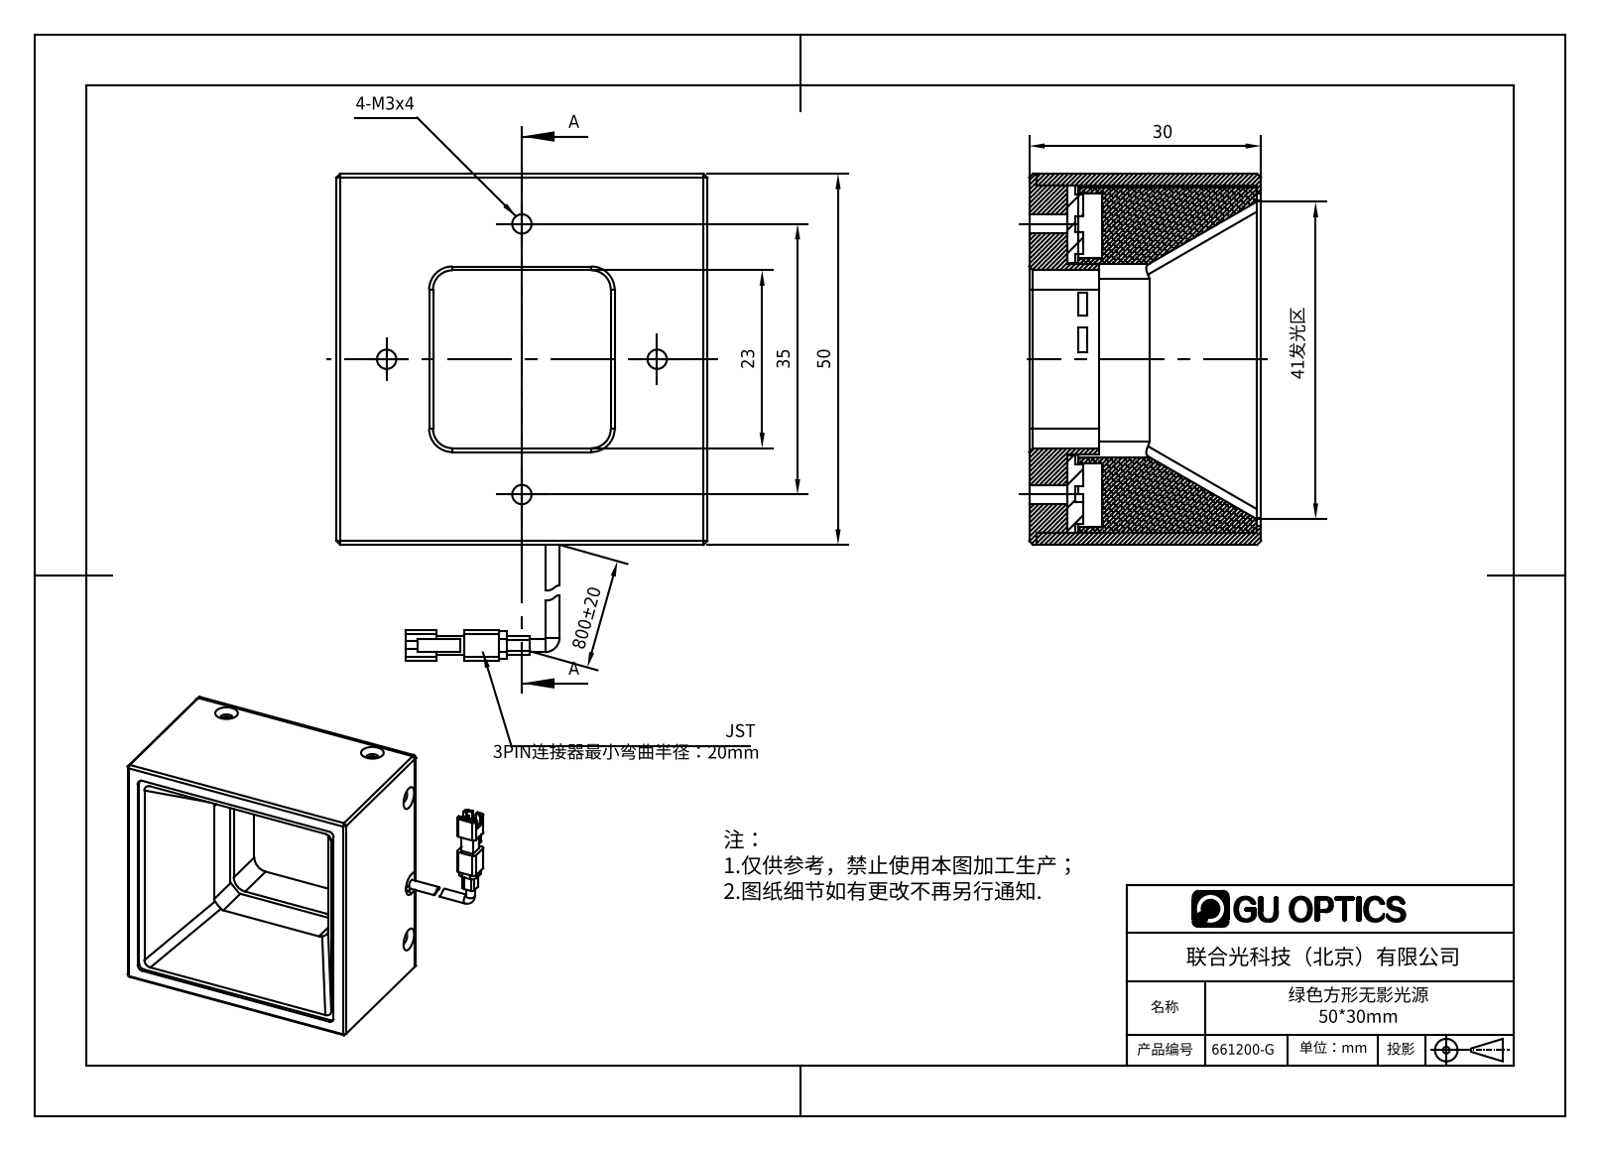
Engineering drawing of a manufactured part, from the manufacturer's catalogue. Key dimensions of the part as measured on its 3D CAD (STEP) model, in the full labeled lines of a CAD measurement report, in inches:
Part name (STEP PRODUCT): 661200-G
STEP written by: SolidWorks 2016 (AUTOMOTIVE_DESIGN)
Units: inches
Bodies: 6 solids, 678 faces (471 planar, 101 cylindrical, 106 other)
Overall size (bounding box): 2.48 × 1.89 × 1.199
Volume: 2.355 in³ · Surface area: 48.71 in²
Round holes (diameter × count): ⌀0.063 ×6, ⌀0.094 ×4, ⌀0.098 ×4
Round bosses / shafts (diameter × count): ⌀0.069 ×2
Partial cylindrical surfaces — rounded edges, fillets, slot ends (radius × count): R0.02 ×8, R0.039 ×8, R0.059 ×8, R0.079 ×6, R0.098 ×4, R0.11 ×4, R0.036 ×2, R0.065 ×1
Main face-to-face distances: 0.059, 1.831, 1.89, 1.772, 0.197, 0.039, 1.819, 1.76, 0.071, 0.236
Hole centre spacings: 0.974, 1.26, 0.35, 1.378, 1.302, 1.313
